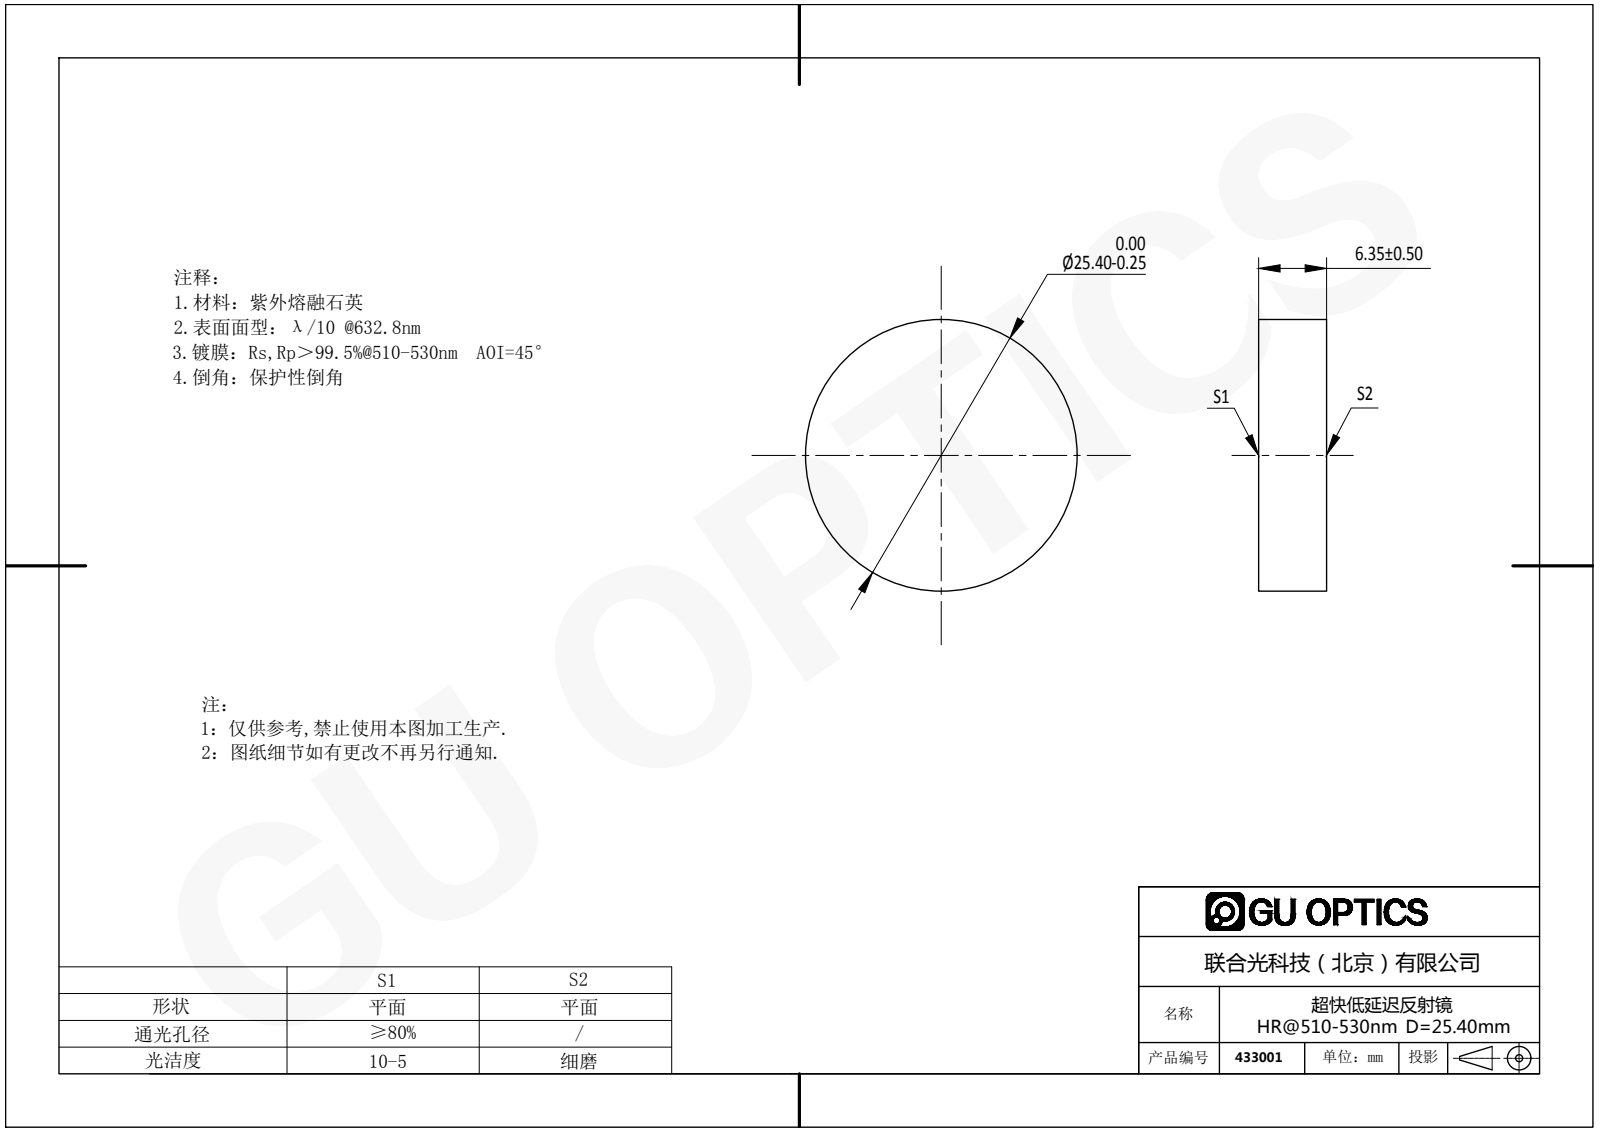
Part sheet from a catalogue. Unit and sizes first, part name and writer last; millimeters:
Units: millimetres
Overall size (bounding box): 25.4 × 25.4 × 6.35
Round bosses / shafts (diameter × count): ⌀25.4 ×1
Main face-to-face distances: 6.35
Volume: 3 218 mm³ · Surface area: 1 520 mm²
Bodies: 1 solid, 4 faces (2 planar, 2 cylindrical, 0 other)
Part name (STEP PRODUCT): 433000
STEP written by: SolidWorks 2016 (AUTOMOTIVE_DESIGN)
